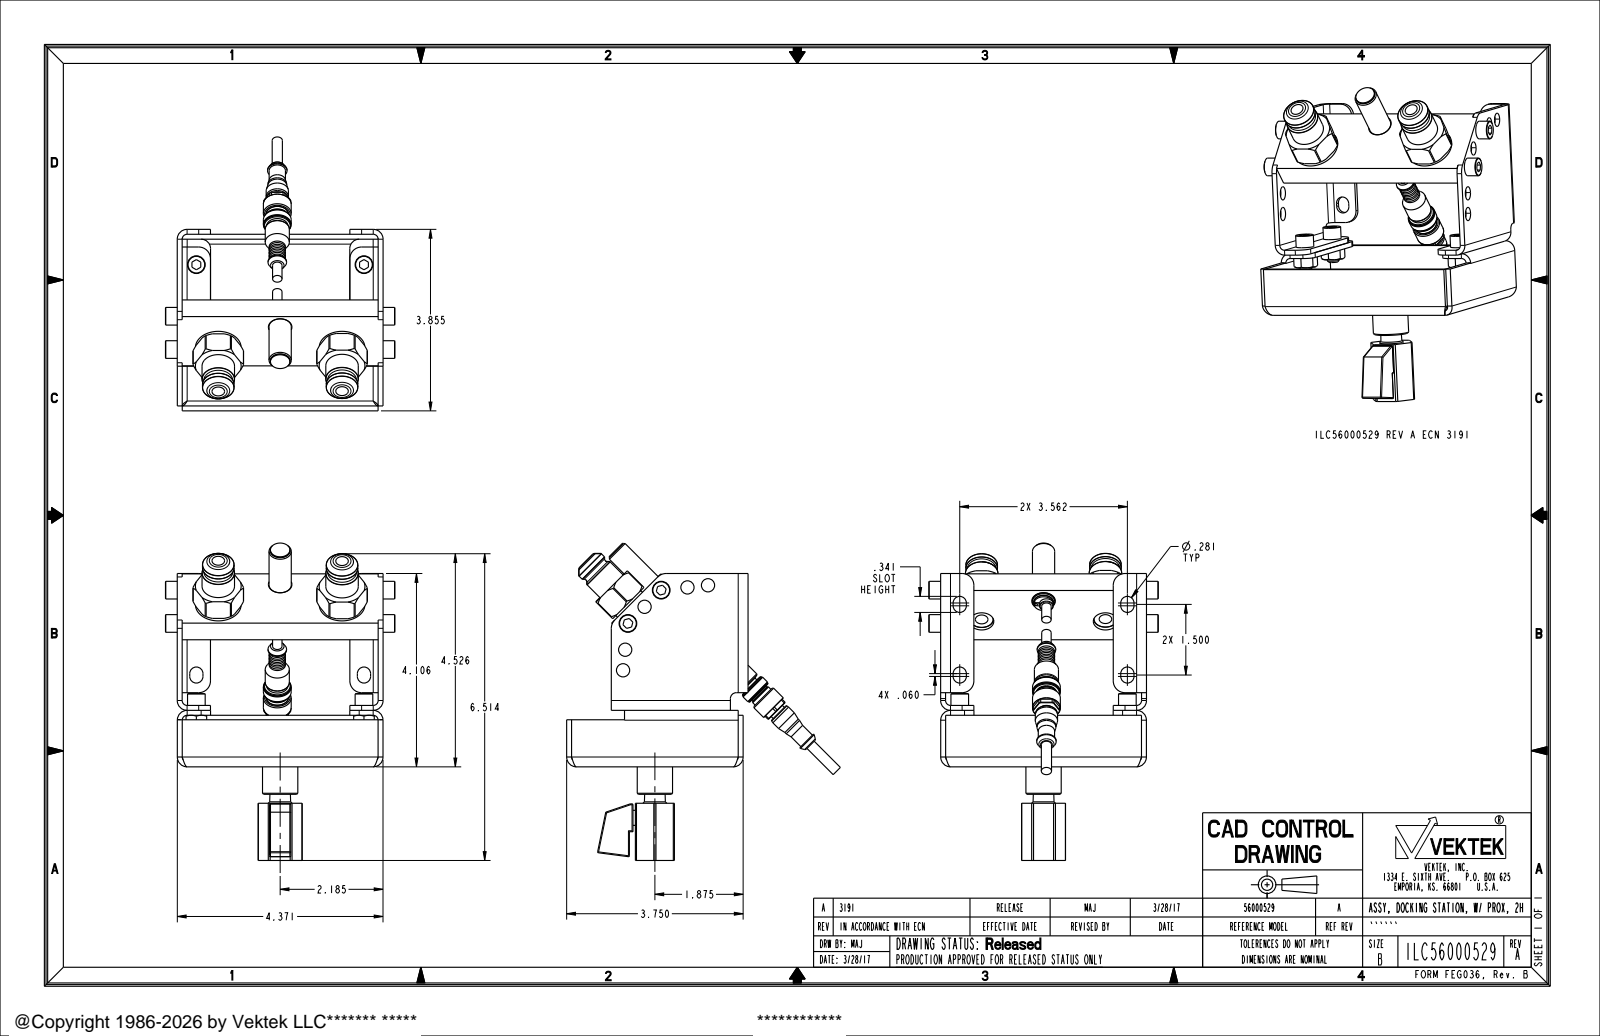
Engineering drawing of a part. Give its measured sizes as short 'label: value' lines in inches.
name: ILC56000529
written by: PRO/ENGINEER BY PARAMETRIC TECHNOLOGY CORPORATION, 2013320 (AUTOMOTIVE_DESIGN)
unit: in
bodies: 4 solids, 743 faces (283 planar, 230 cylindrical, 230 other)
size: 6.925 × 6.446 × 4.874
volume: 11.81 in³; area: 159.5 in²
holes: 5× ⌀0.281, 2× ⌀0.266, 2× ⌀0.515, 2× ⌀0.97, 1× ⌀0.315, 1× ⌀0.443, 1× ⌀0.781
bosses: 6× ⌀0.375, 4× ⌀0.25, 3× ⌀0.75, 2× ⌀0.69, 2× ⌀0.671, 2× ⌀0.413, 1× ⌀0.591, 1× ⌀0.571
rounds: 18× R0.02, 10× R0.105, 10× R0.209, 10× R0.25, 8× R0.141, 4× R0.2, 2× R0.536, 1× R0.125
face distances: 0.105, 4.269, 4.268, 3.645, 4.374, 0.106, 4.163, 4.165, 0.5, 0.103
hole spacings: 0.439, 1, 1.423, 2.229, 1.871, 2.553, 2.63
